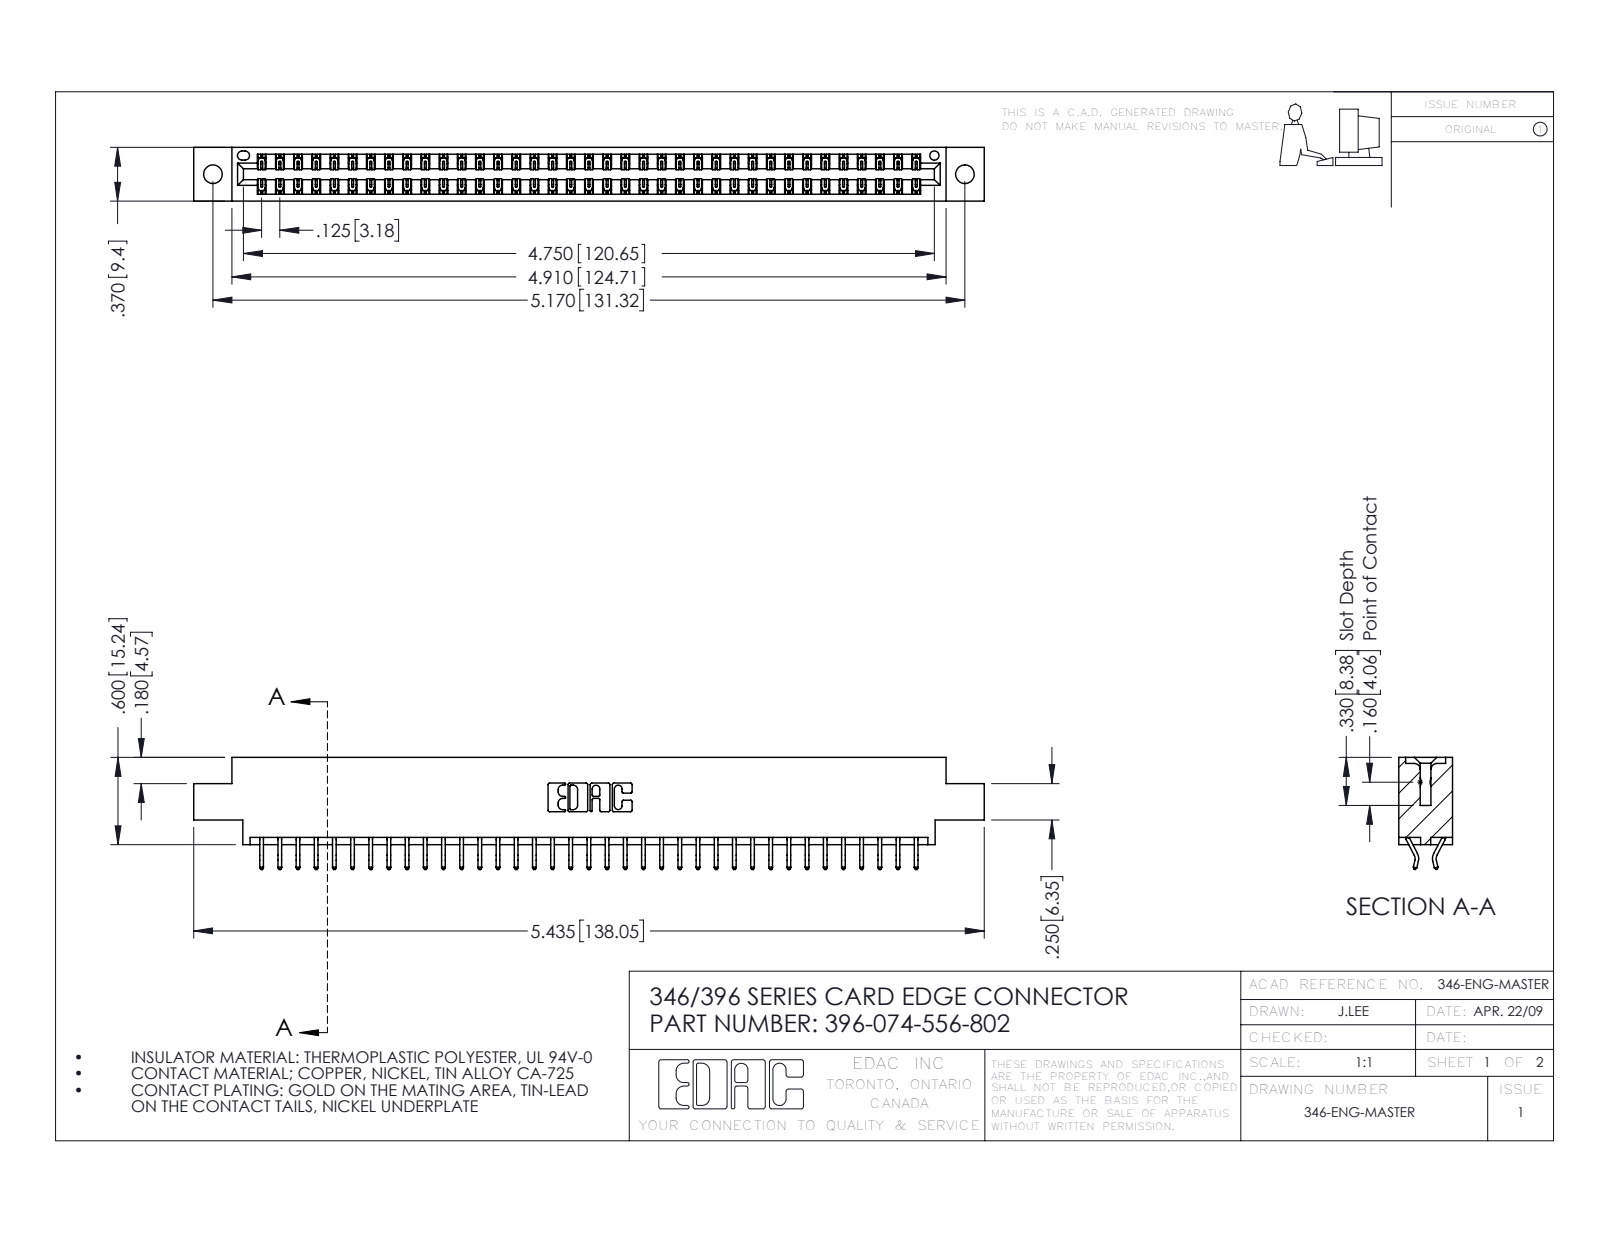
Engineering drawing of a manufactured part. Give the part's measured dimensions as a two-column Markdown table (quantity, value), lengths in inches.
| quantity | value |
| --- | --- |
| part name | 345-292-001_556 Tail; 396-074-556-802; 346 Part_0.170 Offset - 0.128 Dia |
| STEP written by | SolidWorks 2016 (CONFIG_CONTROL_DESIGN) |
| units | inches |
| bodies | 75 solids, 4418 faces (2966 planar, 1452 cylindrical, 0 other) |
| overall size | 5.435 × 0.77 × 0.37 |
| volume | 0.807 in³ |
| surface area | 27.82 in² |
| round holes (diameter × count) | 0.128 × 2, 0.064 × 1 |
| partial cylindrical surfaces (radius × count) | 0.006 × 111, 0.01 × 22, 0.007 × 6, 0.031 × 6, 0.026 × 3, 0.01 × 2, 0.014 × 2, 0.022 × 2 |
| main face-to-face distances | 0.048, 0.322, 0.37, 0.25, 0.025, 0.072, 0.298, 0.275, 0.148, 0.222 |
| hole center spacings | 0.246, 4.961, 5.17 |
